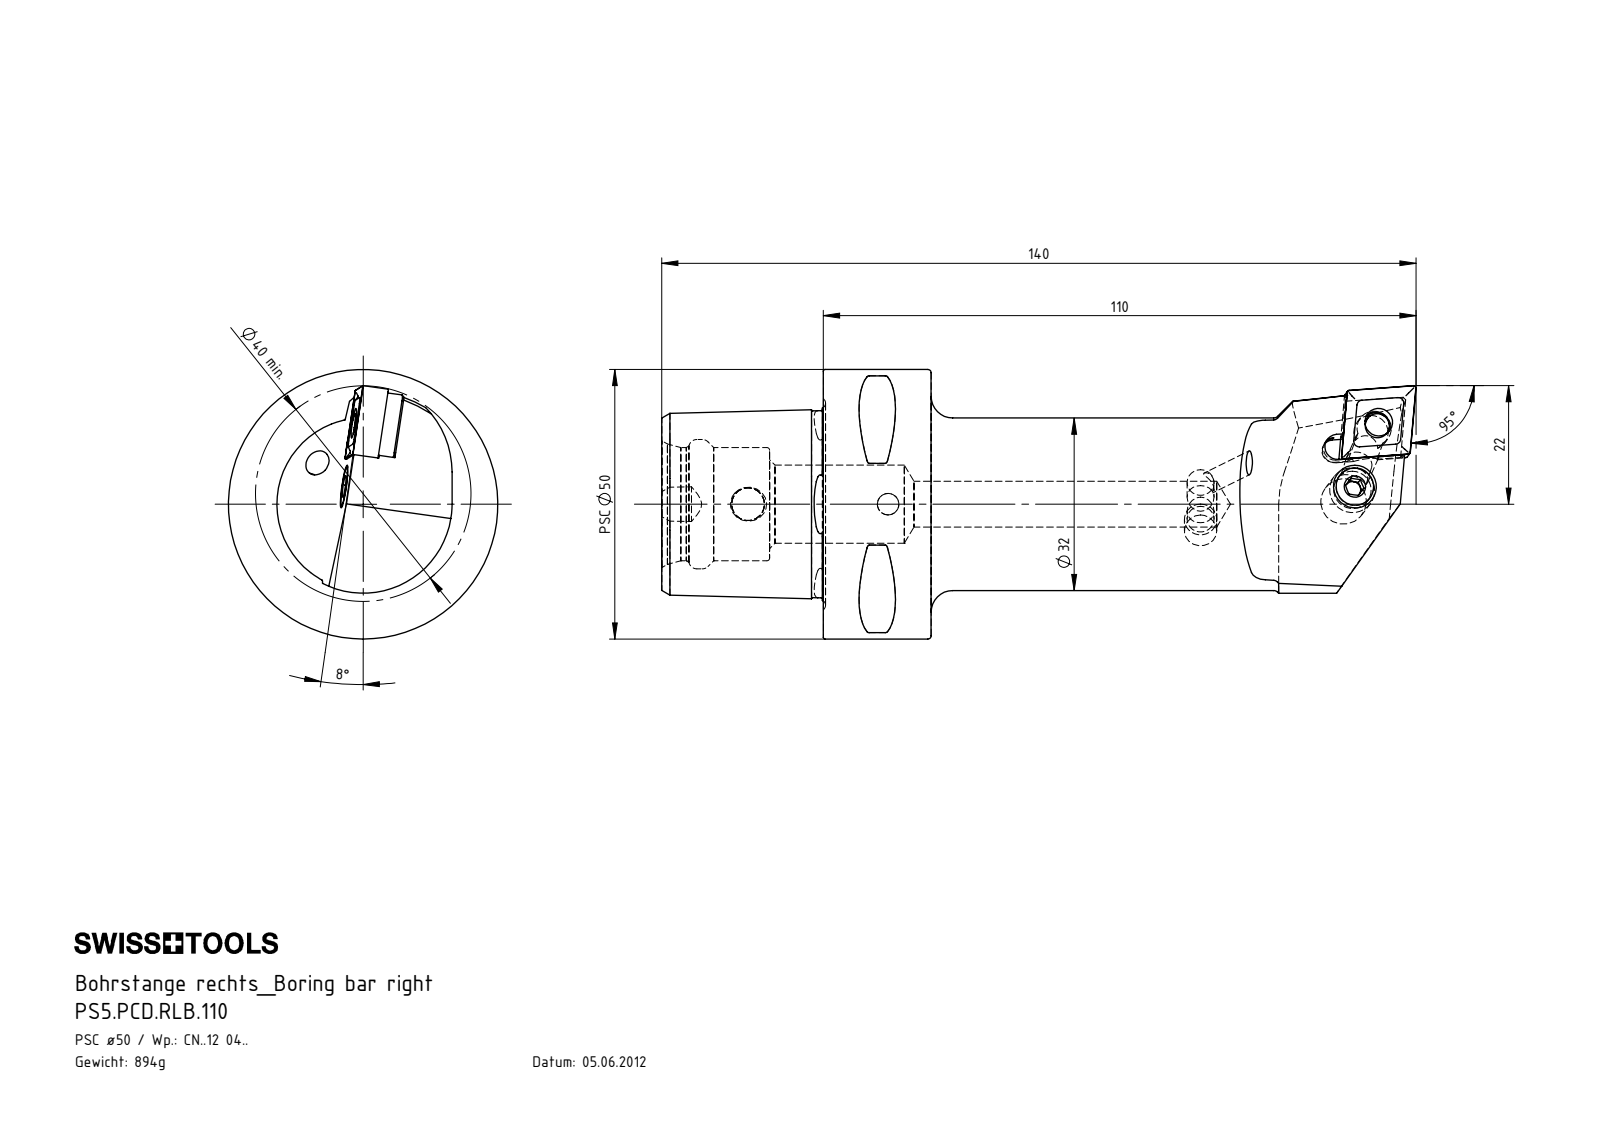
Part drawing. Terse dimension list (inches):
name: CNMG120404; WCD-ER2.101.003_A; PS5.PCD.RLB.110; WCD-ER1.101.000 (+4 more)
written by: SolidWorks 2017 (AUTOMOTIVE_DESIGN)
unit: in
bodies: 9 solids, 362 faces (96 planar, 93 cylindrical, 173 other)
size: 5.512 × 1.969 × 1.969
volume: 6.9 in³; area: 40.6 in²
holes: 1× ⌀0.157, 1× ⌀0.165, 1× ⌀0.197, 1× ⌀0.203, 1× ⌀0.24, 1× ⌀0.252, 1× ⌀0.276, 1× ⌀0.331, 1× ⌀0.335, 1× ⌀0.571, 1× ⌀0.827, 1× ⌀0.945
bosses: 1× ⌀1.969, 1× ⌀1.26, 1× ⌀0.315, 1× ⌀0.311, 1× ⌀0.252, 1× ⌀0.236, 1× ⌀0.177, 1× ⌀0.14
rounds: 8× R0.02, 4× R0.016, 4× R0.039, 2× R0.098, 1× R0.083, 1× R0.087, 1× R0.093, 1× R0.11
face distances: 0.787, 1.181, 1.969, 0.175, 0.755, 1.748, 0.012, 0.301, 0.394, 0.02
hole spacings: 0.504, 0.507, 1.024
